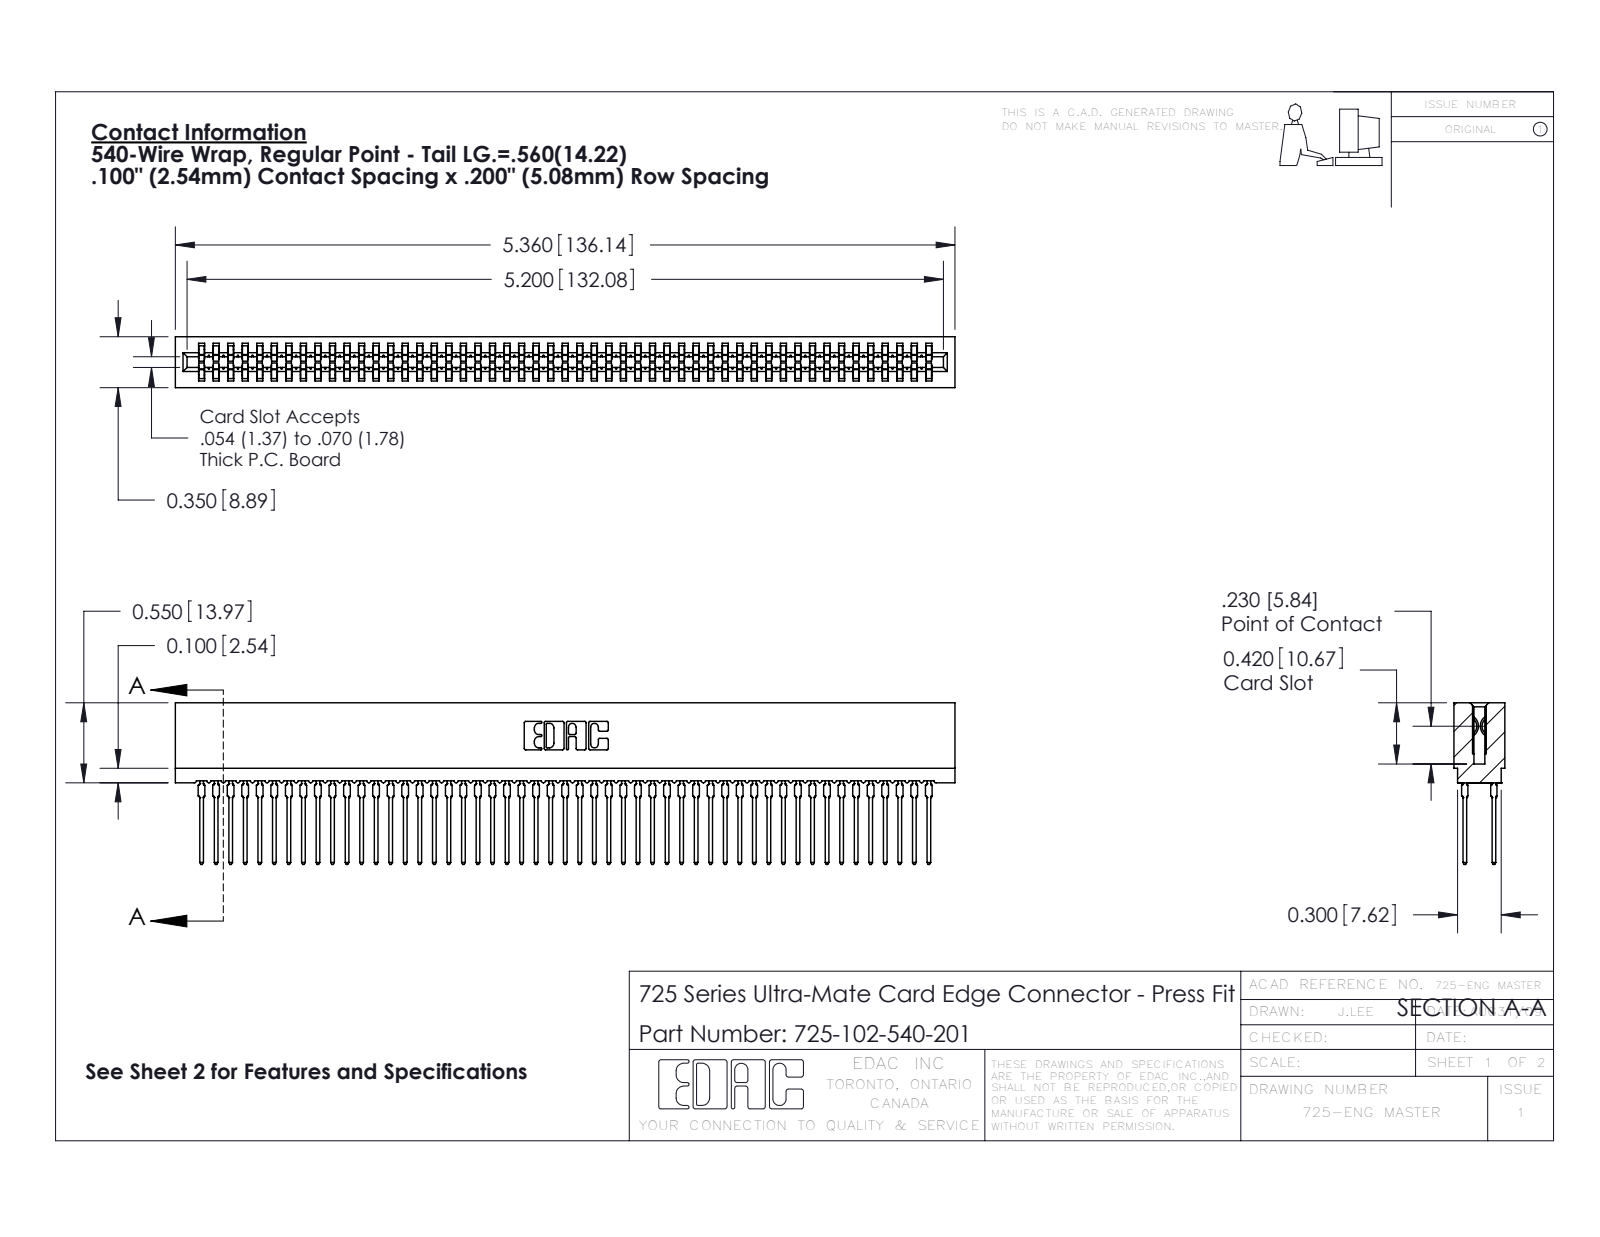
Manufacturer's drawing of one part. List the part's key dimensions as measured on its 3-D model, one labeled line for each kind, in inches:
Part name (STEP PRODUCT): 745-292-001_540; 725 Part_Insulator Option - 01; 725-102-540-201
STEP written by: SolidWorks 2016 (CONFIG_CONTROL_DESIGN)
Units: inches
Bodies: 103 solids, 9224 faces (4747 planar, 1825 cylindrical, 2652 other)
Overall size (bounding box): 5.36 × 1.11 × 0.35
Volume: 0.674 in³ · Surface area: 38.31 in²
Partial cylindrical surfaces — rounded edges, fillets, slot ends (radius × count): R0.021 ×204, R0.015 ×102, R0.01 ×22, R0.005 ×8, R0.011 ×8, R0.007 ×6, R0.031 ×6, R0.026 ×3
Main face-to-face distances: 0.2, 0.063, 0.287, 0.35, 0.212, 0.138, 0.076, 0.149, 0.087, 0.263
